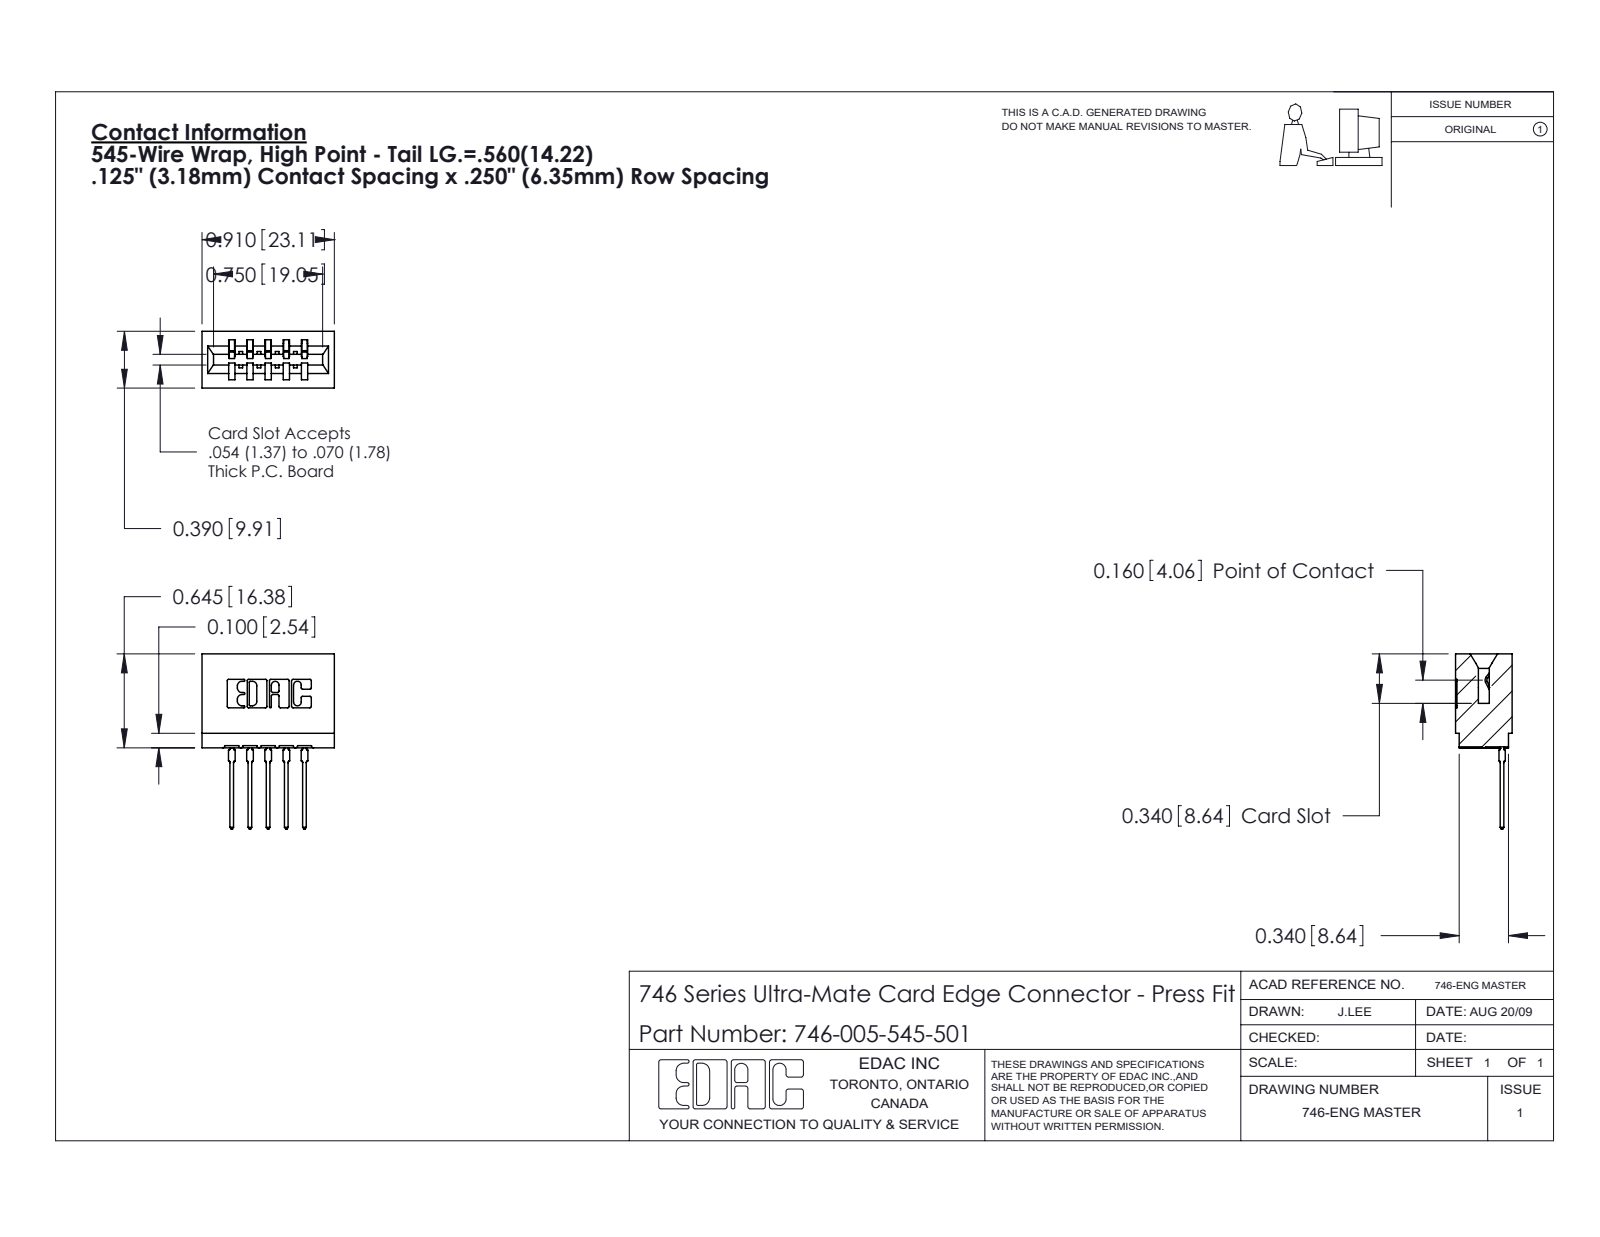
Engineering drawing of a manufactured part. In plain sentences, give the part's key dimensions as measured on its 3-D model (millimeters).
The part is named "746 Part_.340 Slot Depth - 01; 746-005-545-501; 746-292-001_545". Its 3-D file was written by "SolidWorks 2020 (CONFIG_CONTROL_DESIGN)". It is 6 solids with 637 faces: 370 planar, 137 cylindrical and 130 other. Overall it measures 30.6 by 23.1 by 9.9 millimeters. Its volume is 2 830 cubic millimeters and its surface area 3 330 square millimeters. Partial cylindrical surfaces (rounded edges, fillets, slot ends): 22 of radius 0.3, 10 of radius 0.5, 6 of radius 0.2, 6 of radius 0.4, 6 of radius 0.8, 4 of radius 0.1, 4 of radius 0.3, 3 of radius 0.7. The main face-to-face distances are 6.4, 1.1, 8.5, 3.2, 3.2, 1.4, 9.9, 2.1, 7.4, 5.3.
